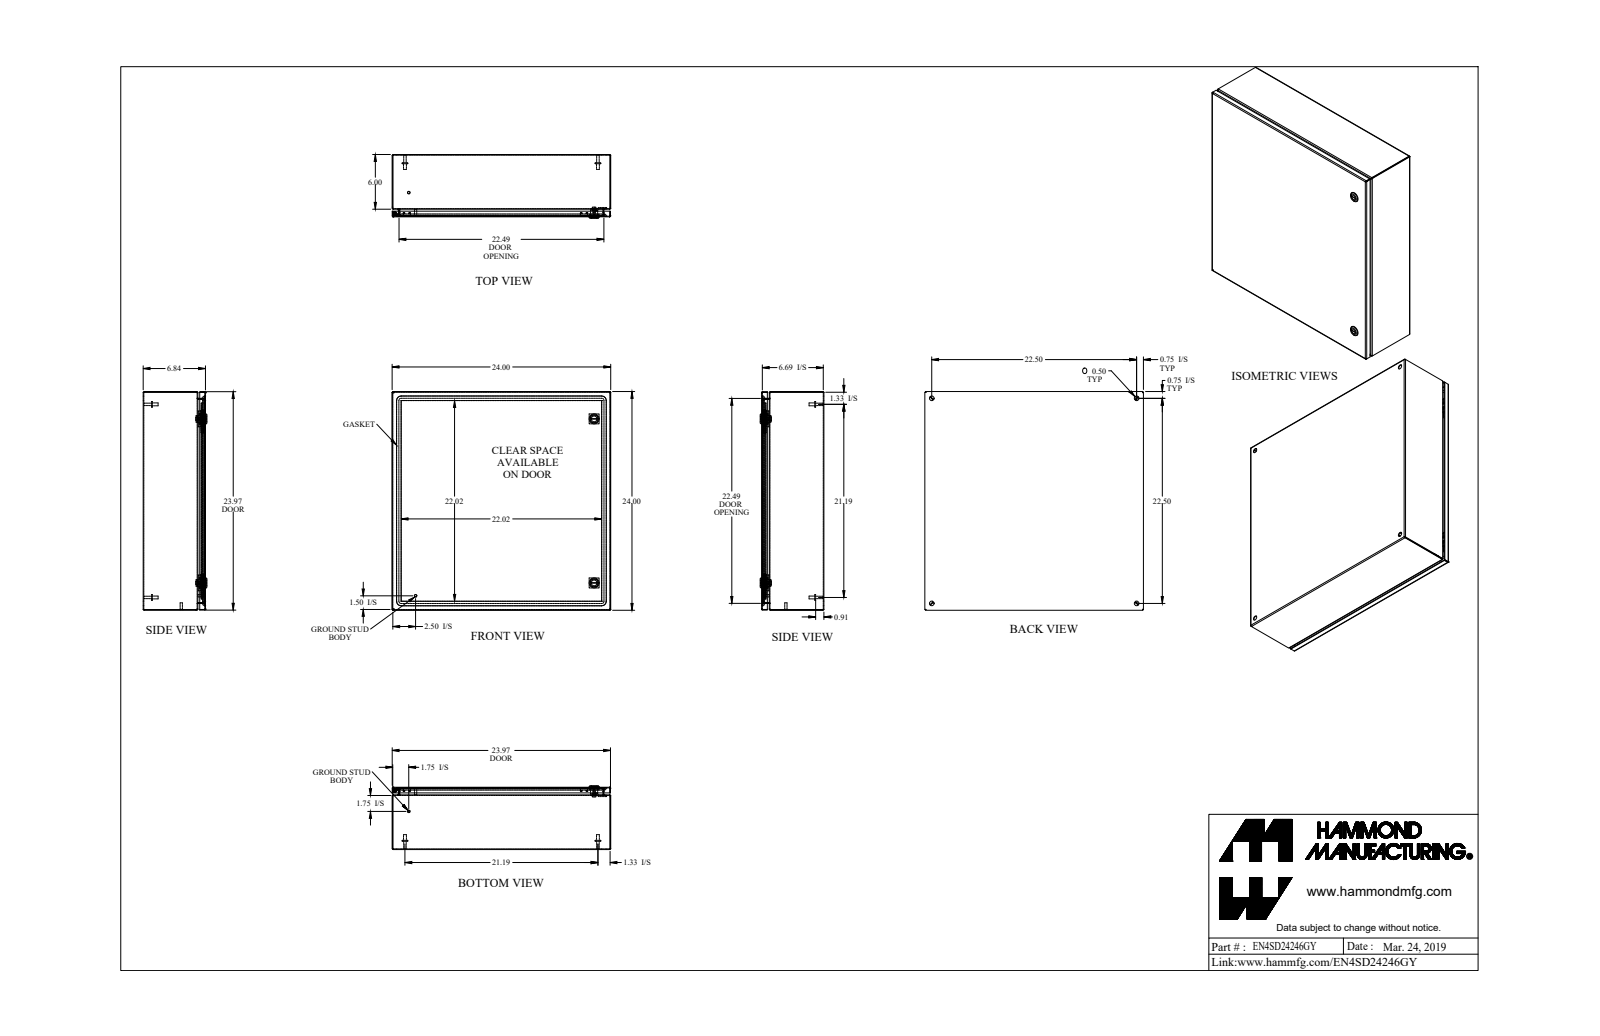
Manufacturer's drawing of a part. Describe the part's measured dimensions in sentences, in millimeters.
The part is named "EN4SD24246GY_Default". Its 3-D file was written by "SolidWorks 2019 (CONFIG_CONTROL_DESIGN)". It is 27 solids with 783 faces: 386 planar, 257 cylindrical and 140 other. Overall it measures 609.6 by 609.6 by 177.7 millimeters. Its volume is 2 461 000 cubic millimeters and its surface area 2 714 000 square millimeters. Round holes: 4 of diameter 12.7, 2 of diameter 5.9, 2 of diameter 15.9, 2 of diameter 19.9, 1 of diameter 4.4, 1 of diameter 6.1, 1 of diameter 6.1. Round bosses or shafts: 4 of diameter 15.9, 4 of diameter 8, 4 of diameter 6.9, 2 of diameter 27.9, 2 of diameter 13.3, 2 of diameter 7.1, 2 of diameter 6.4, 1 of diameter 11.6. Partial cylindrical surfaces (rounded edges, fillets, slot ends): 20 of radius 0.9, 20 of radius 2.7, 12 of radius 1.1, 12 of radius 2.1, 12 of radius 9.7, 8 of radius 482.7, 4 of radius 0.2, 4 of radius 1.6. The main face-to-face distances are 1.8, 171.8, 170, 173.7, 607.8, 605.9, 609.6, 21.3, 150.6, 19.1. The hole center spacings are 571.5, 808.2, 63.3, 63.3, 457.2, 515, 515.1, 547.2.
